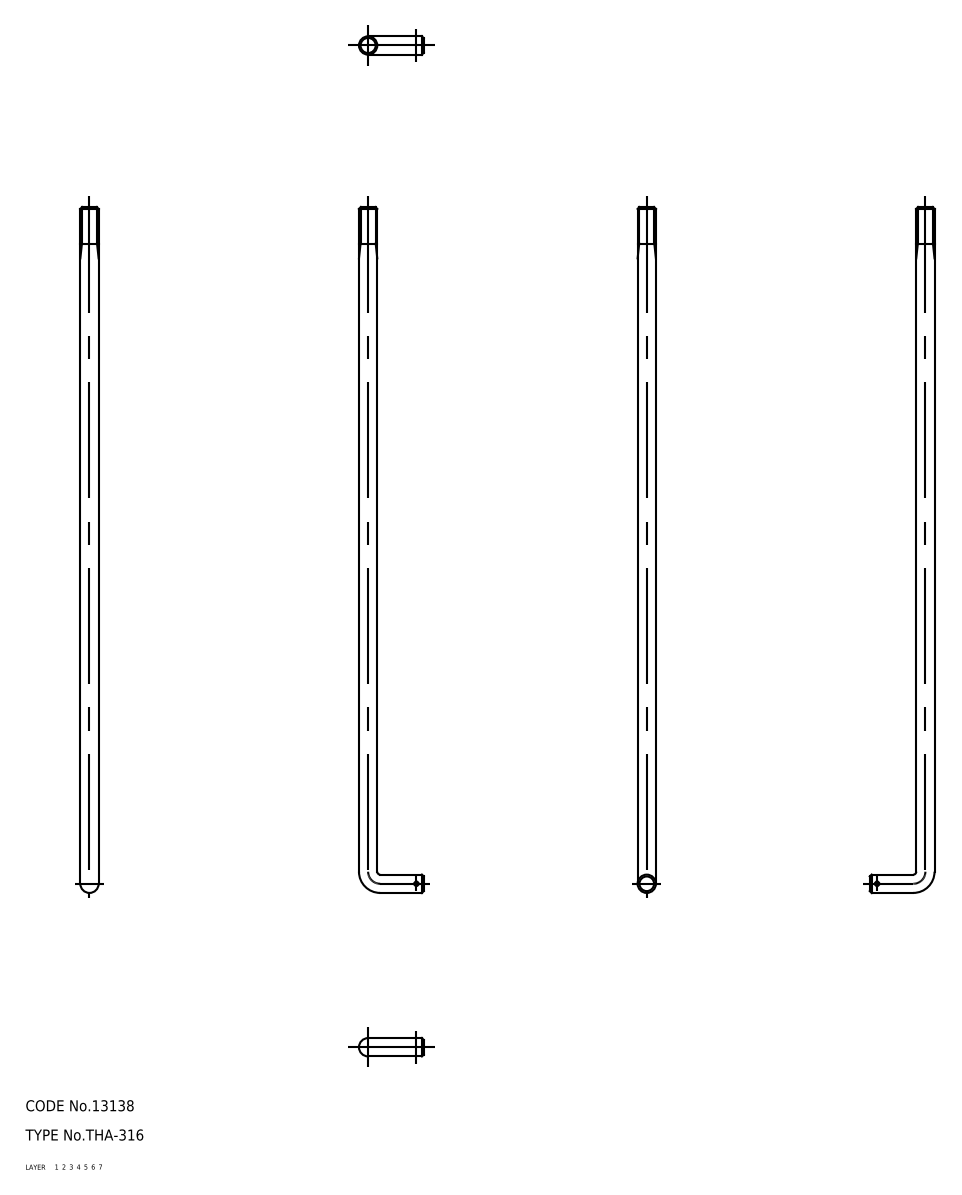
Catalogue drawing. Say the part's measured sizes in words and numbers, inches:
The part is named "rod". Its 3-D file was written by "CADfix (AUTOMOTIVE_DESIGN)". It is 1 solid with 14 faces: 0 planar, 0 cylindrical and 14 other. Overall it measures 7.382 by 0.697 by 0.197 inches. Its volume is 0.237 cubic inches and its surface area 4.91 square inches.
